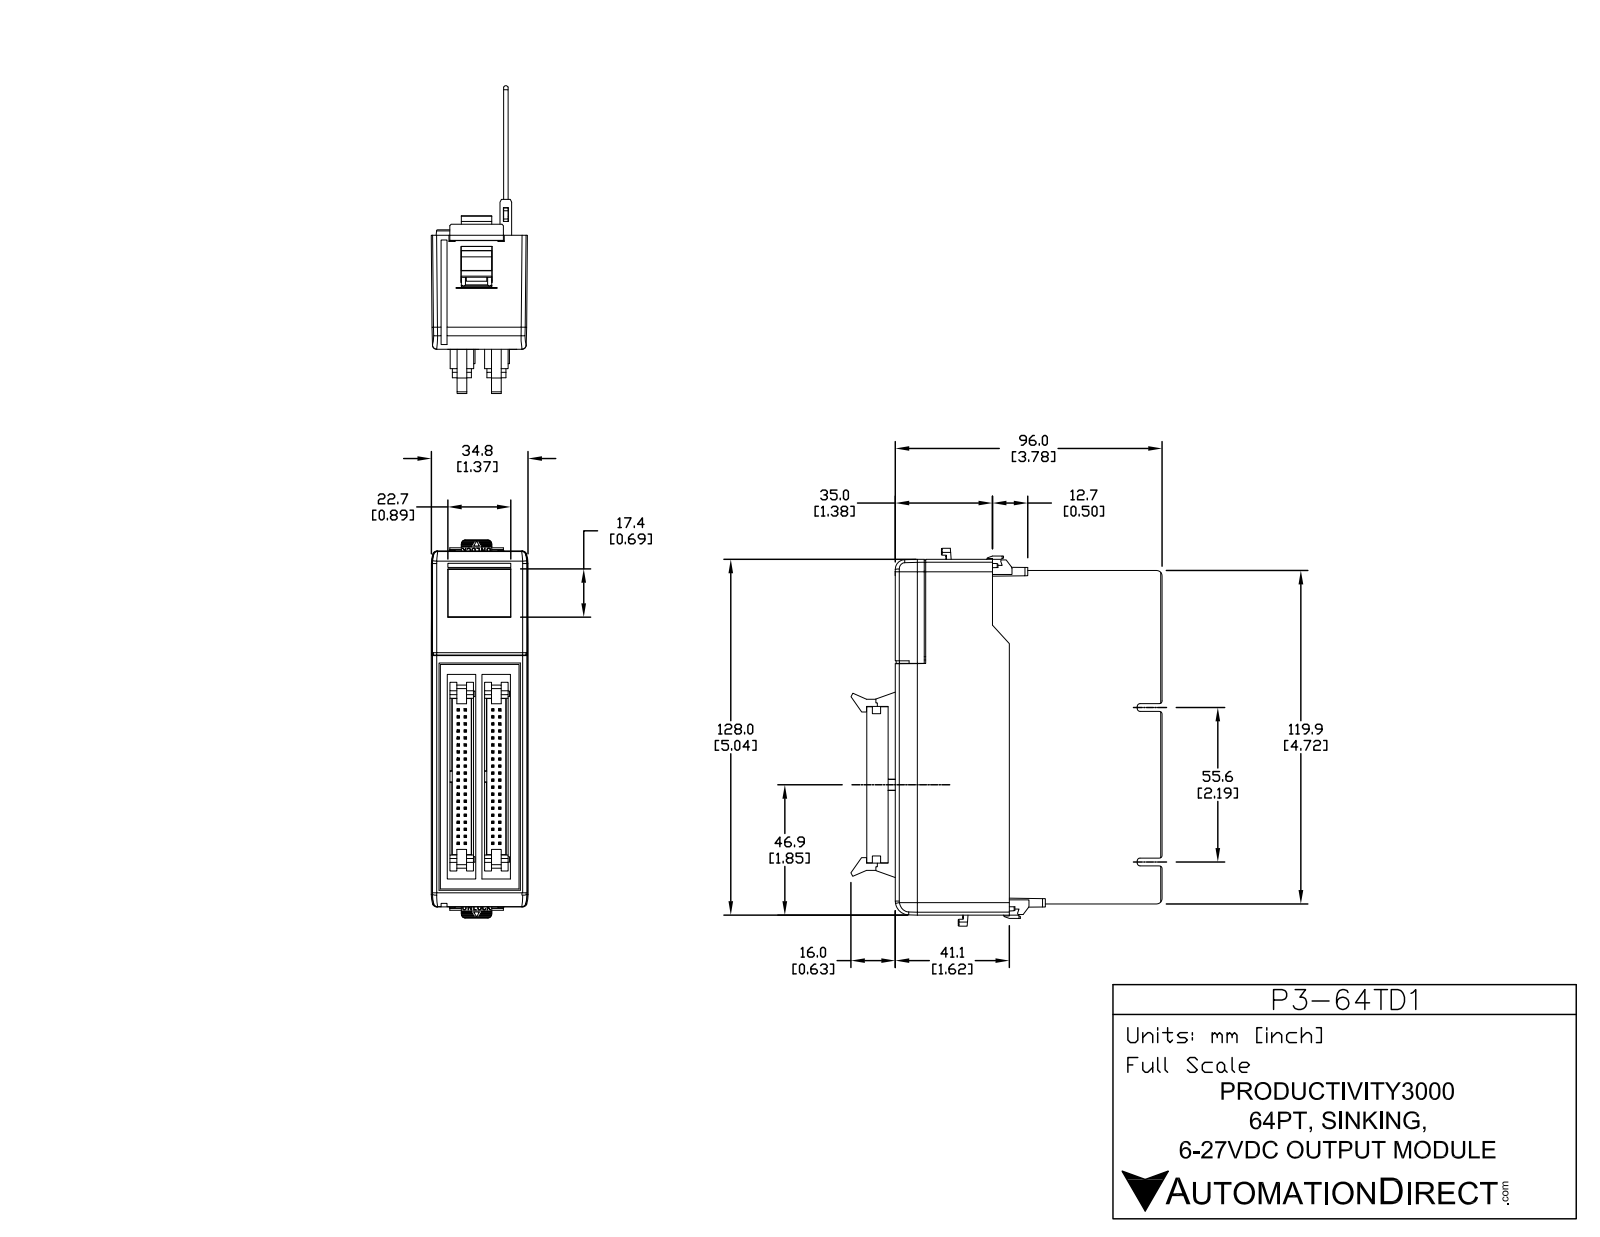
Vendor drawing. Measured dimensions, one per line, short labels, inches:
name: P3-64TD1
written by: SolidWorks 2009 (CONFIG_CONTROL_DESIGN)
unit: in
bodies: 1 solid, 1509 faces (1406 planar, 73 cylindrical, 30 other)
size: 5.357 × 4.405 × 1.37
volume: 11.93 in³; area: 86.16 in²
holes: 2× ⌀0.157
rounds: 25× R0.039, 8× R0.012, 6× R0.02, 6× R0.059, 4× R0.02, 2× R0.004, 2× R0.045, 2× R0.047
face distances: 0.496, 0.063, 0.433, 0.559, 1.623, 0.067, 1.556, 0.307, 0.028, 0.24
hole spacings: 4.184
